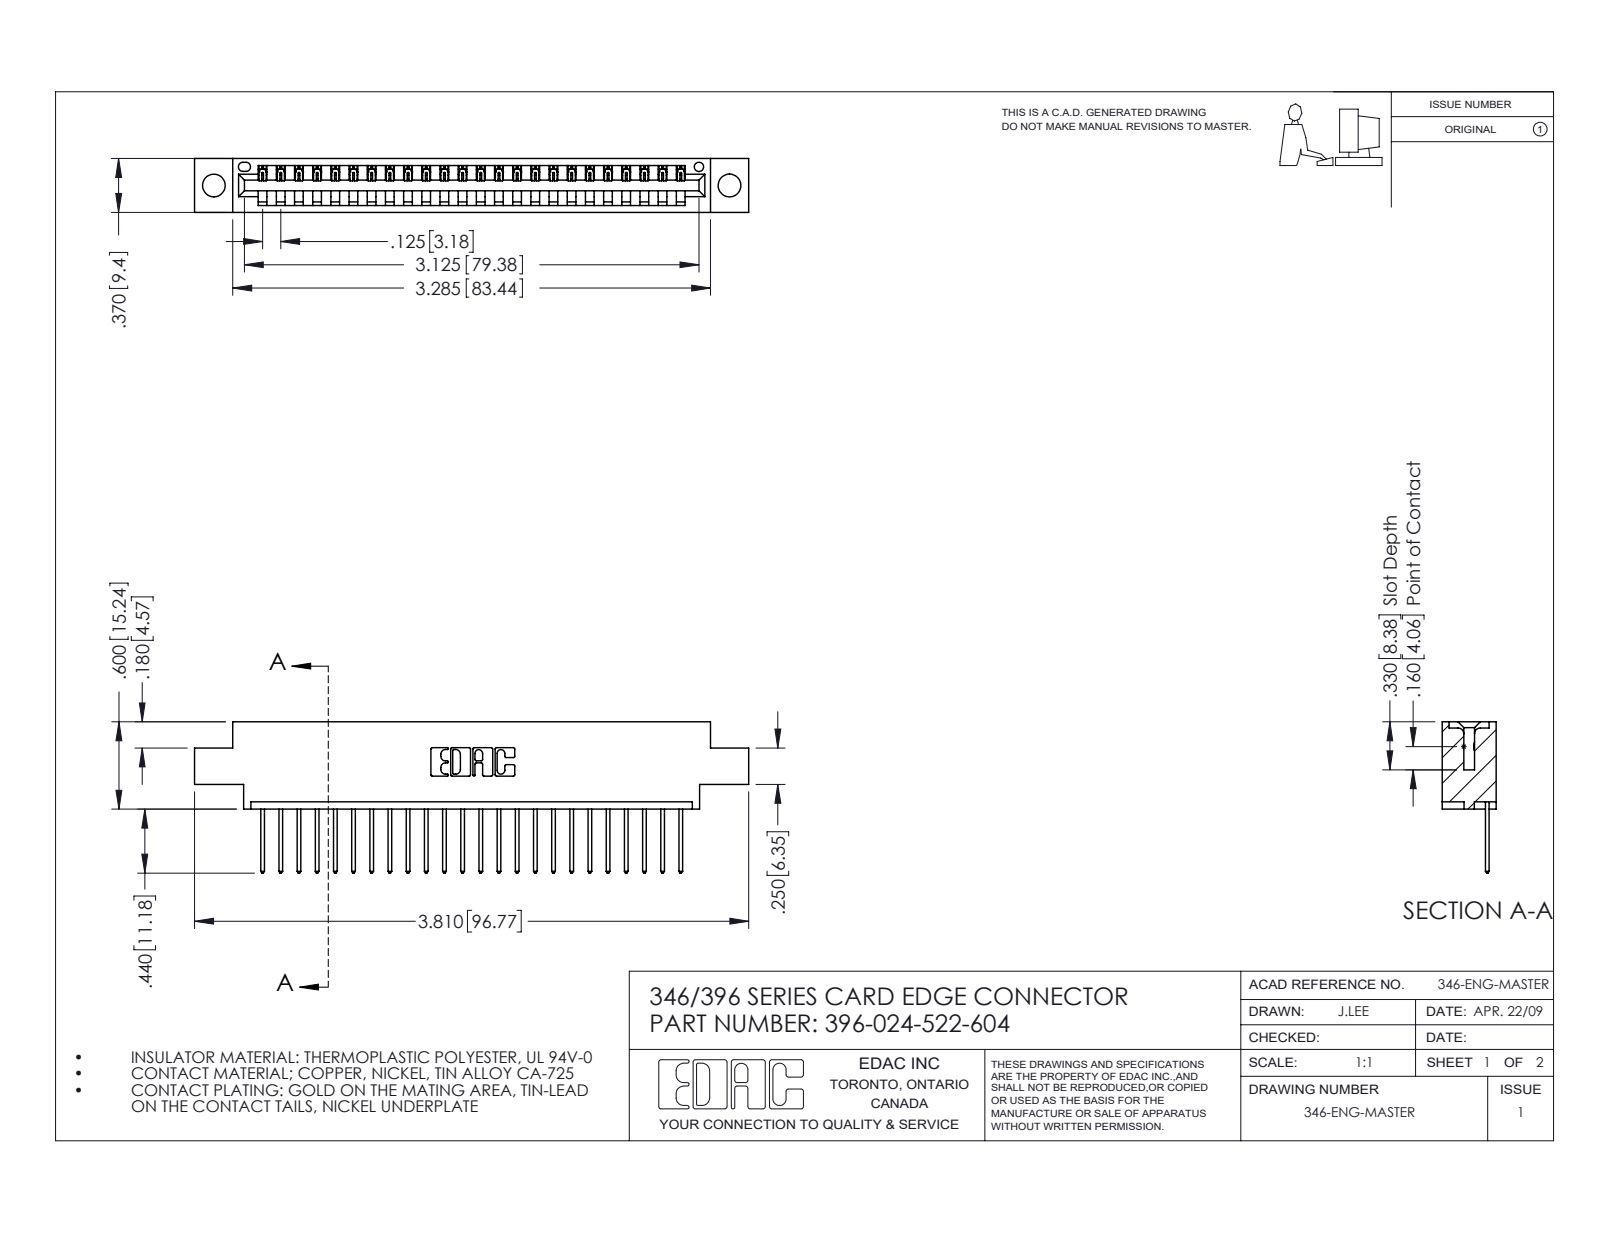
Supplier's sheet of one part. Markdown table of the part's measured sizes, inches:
| quantity | value |
| --- | --- |
| part name | 396-024-522-604; 345-292-001_345-293-122; 346 Part_0.170 Offset - 0.156 Dia-TH |
| STEP written by | SolidWorks 2016 (CONFIG_CONTROL_DESIGN) |
| units | inches |
| bodies | 25 solids, 1518 faces (1040 planar, 478 cylindrical, 0 other) |
| overall size | 3.81 × 1.04 × 0.37 |
| volume | 0.543 in³ |
| surface area | 17.02 in² |
| round holes (diameter × count) | 0.156 × 2, 0.064 × 1 |
| partial cylindrical surfaces (radius × count) | 0.006 × 48, 0.01 × 48, 0.01 × 22, 0.007 × 6, 0.031 × 6, 0.026 × 3, 0.031 × 2, 0.04 × 2 |
| main face-to-face distances | 0.048, 0.322, 0.37, 0.25, 0.072, 0.298, 0.025, 0.148, 0.222, 0.1 |
| hole center spacings | 0.246, 3.337, 3.545 |
